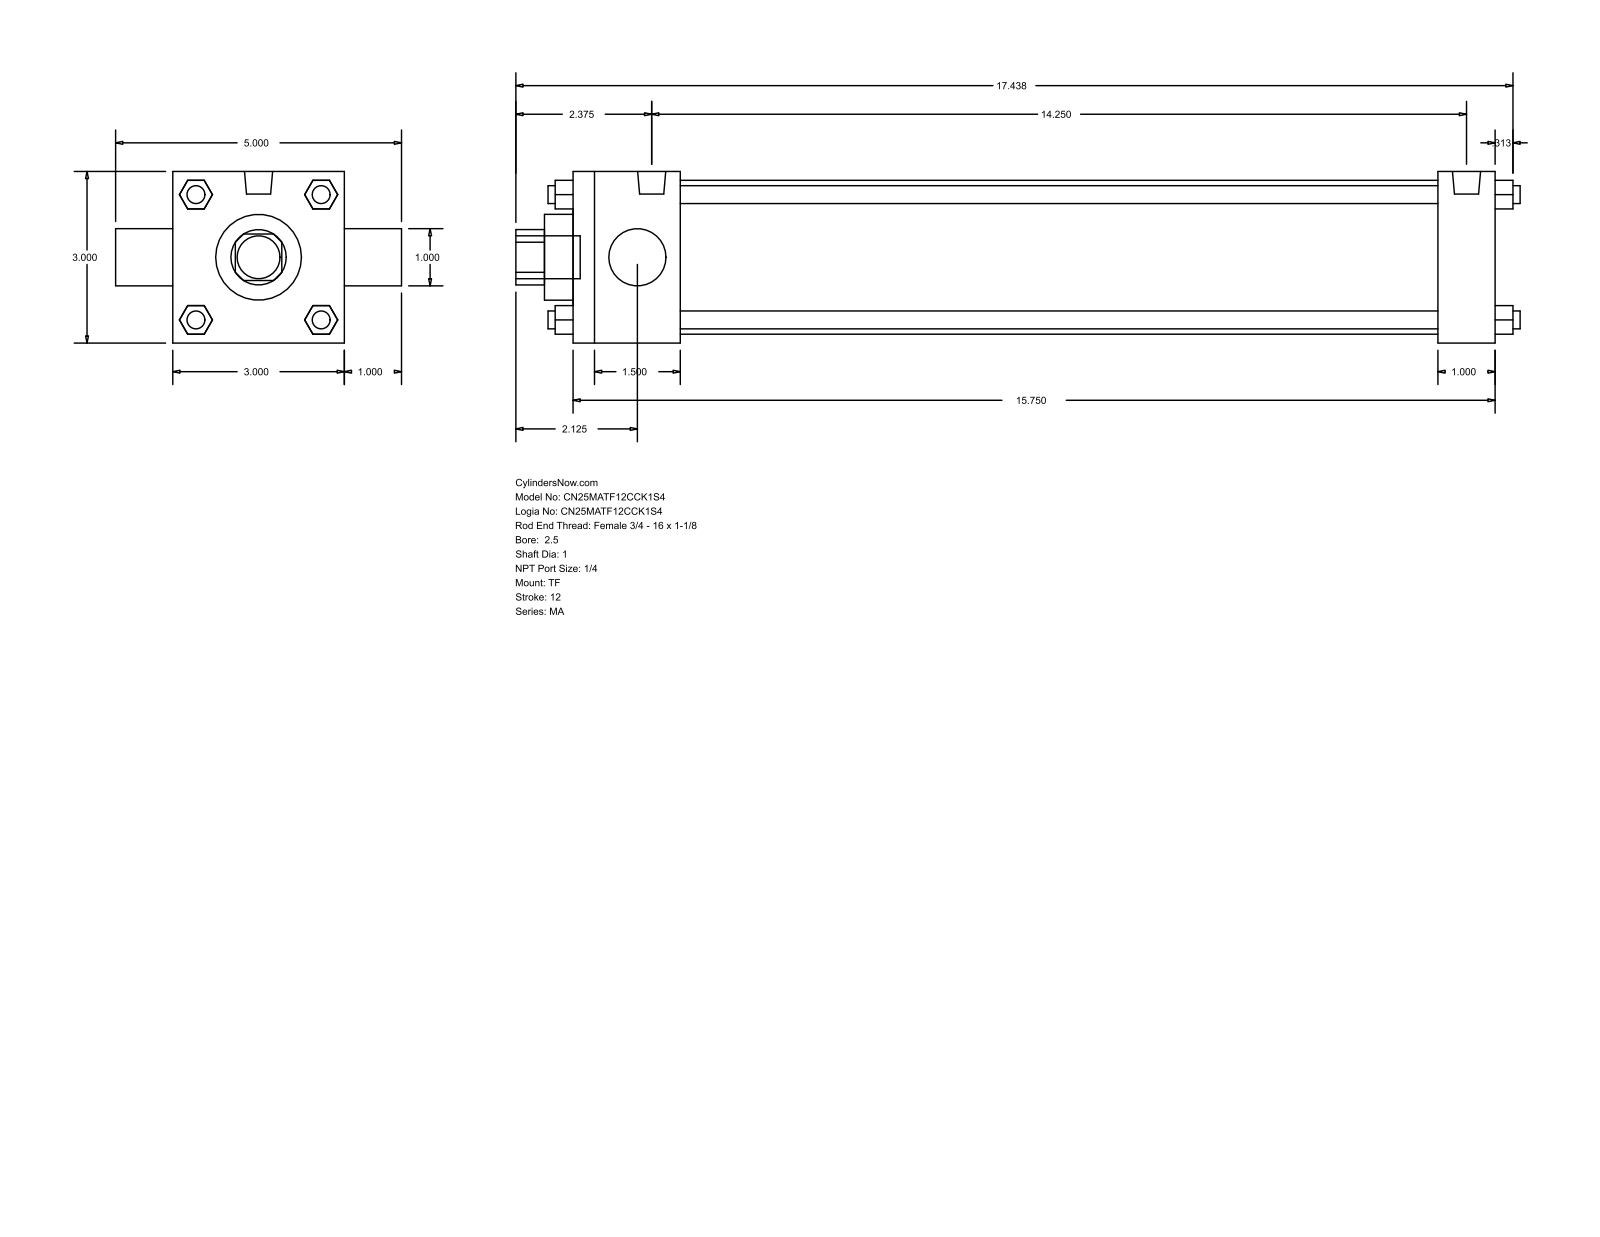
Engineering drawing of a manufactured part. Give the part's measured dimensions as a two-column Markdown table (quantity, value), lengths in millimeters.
| quantity | value |
| --- | --- |
| part name | MA_TF__0250_1 |
| STEP written by | GSSL Pune (CONFIG_CONTROL_DESIGN) |
| units | millimeters |
| bodies | 0 solids, 120 faces (92 planar, 28 cylindrical, 0 other) |
| overall size | 446.09 × 127 × 76.2 |
| round holes (diameter × count) | 25.4 × 2, 38.1 × 1, 68.33 × 1 |
| round bosses / shafts (diameter × count) | 7.94 × 7, 12.49 × 2, 19.05 × 1 |
| partial cylindrical surfaces (radius × count) | 12.29 × 1 |
| main face-to-face distances | 76.2, 409.58, 12.7, 47.63, 384.17, 336.54, 361.95, 25.41, 25.4, 101.6 |
